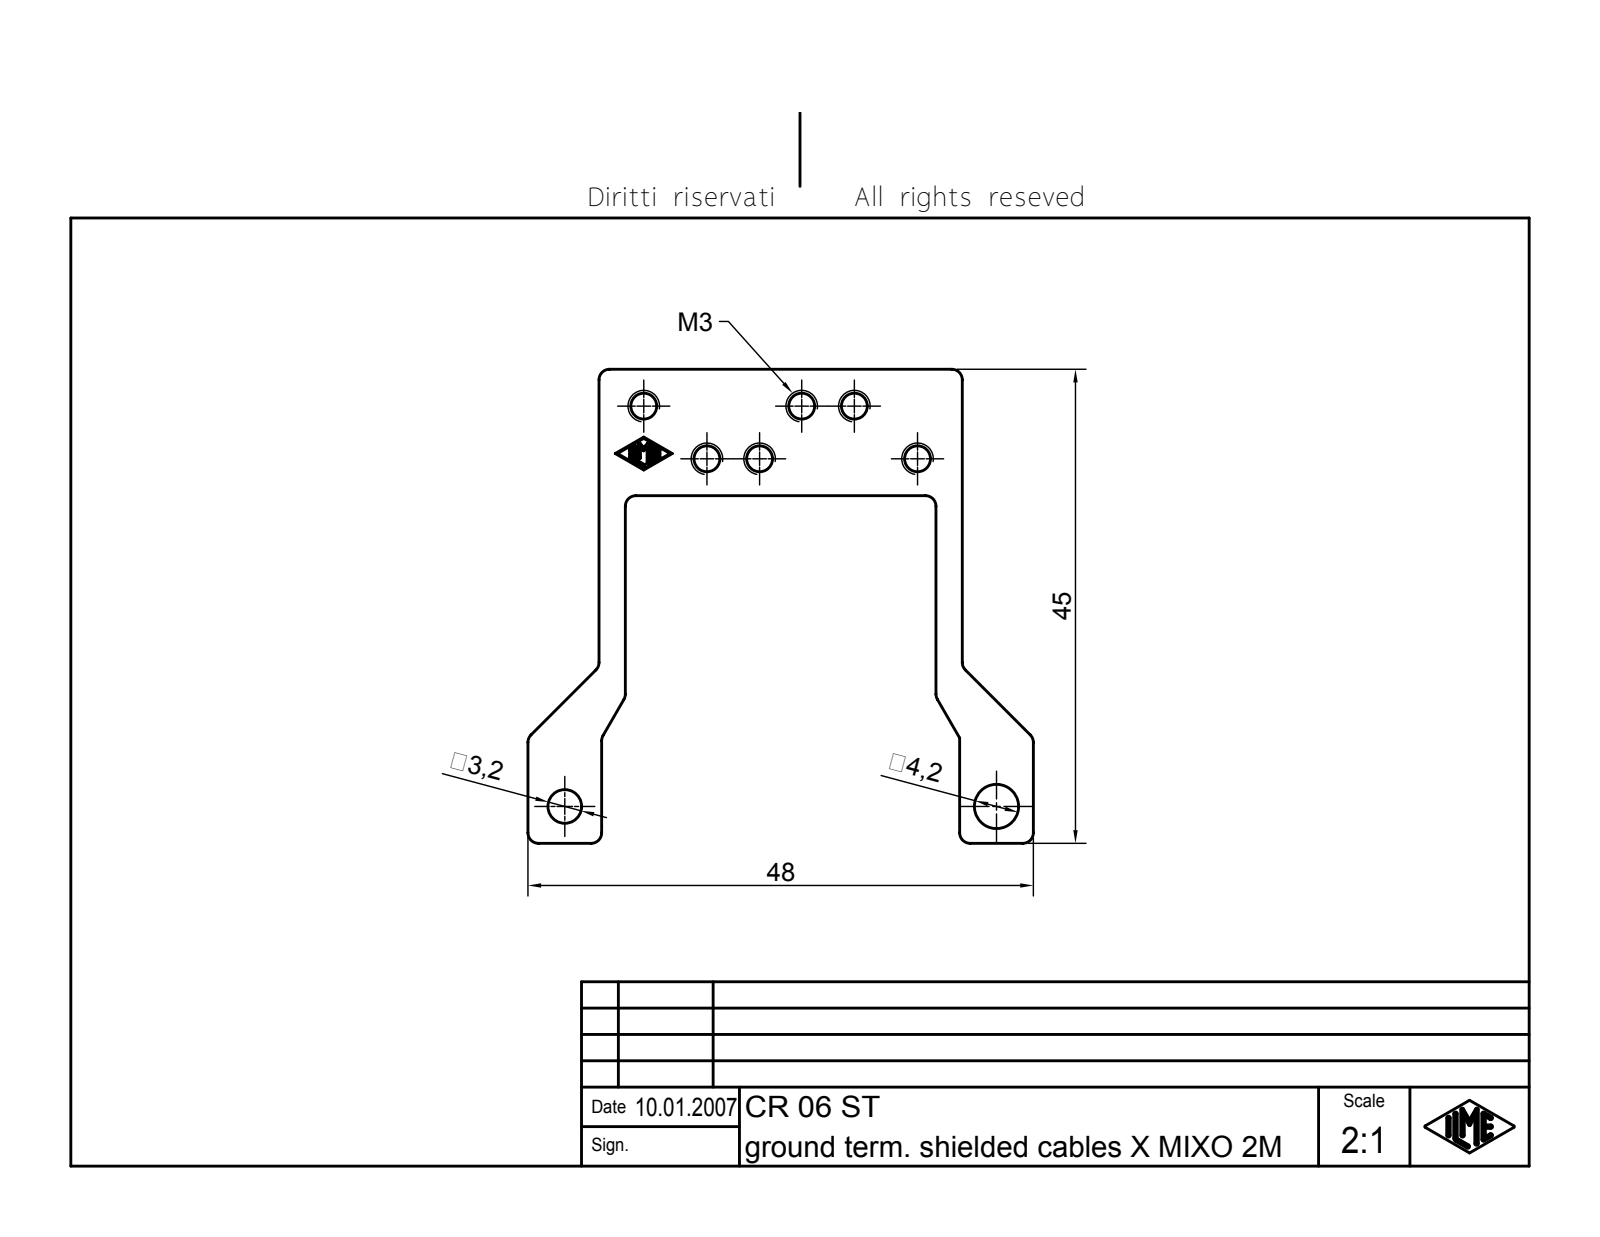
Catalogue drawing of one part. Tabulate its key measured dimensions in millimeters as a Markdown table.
| quantity | value |
| --- | --- |
| part name | CR 06 ST |
| STEP written by | Autodesk Inventor 7 (AUTOMOTIVE_DESIGN) |
| units | millimeters |
| bodies | 1 solid, 115 faces (55 planar, 48 cylindrical, 12 other) |
| overall size | 48 × 45 × 2 |
| volume | 1 308 mm³ |
| surface area | 1 932 mm² |
| round holes (diameter × count) | 3.2 × 1, 4.2 × 1 |
| partial cylindrical surfaces (radius × count) | 1 × 15, 0.1 × 14 |
| main face-to-face distances | 2, 2.5, 32, 12, 34.5, 29.5, 34.25, 2.25, 31.75, 6.75 |
| hole center spacings | 41 |
